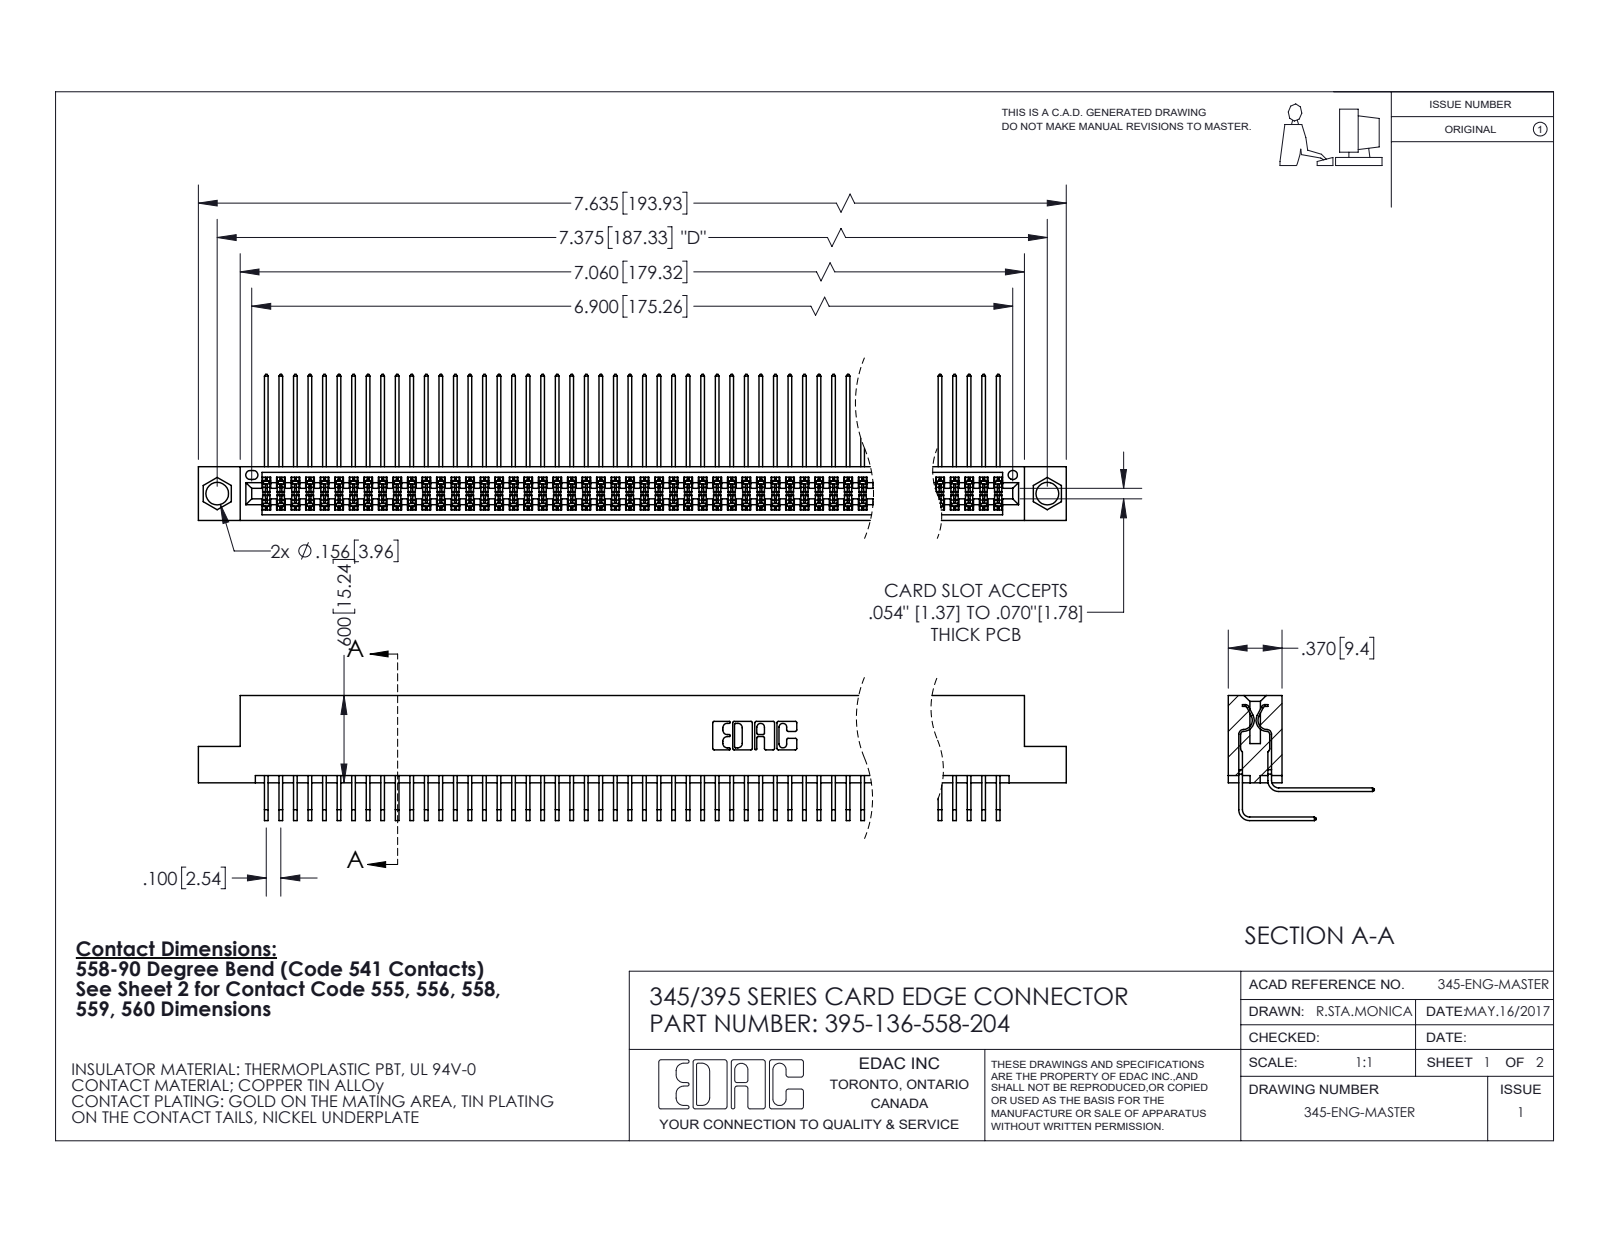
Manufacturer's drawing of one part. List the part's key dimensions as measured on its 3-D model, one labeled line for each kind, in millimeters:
Part name (STEP PRODUCT): 345 Part_Flush Mounting Lugs - 0.156 Dia-TI; 345-292-001_558 559 Tail - 1; 395-136-558-204; 345-292-001_558 Tail - 2
STEP written by: SolidWorks 2020 (CONFIG_CONTROL_DESIGN)
Units: millimetres
Bodies: 137 solids, 7212 faces (4854 planar, 2358 cylindrical, 0 other)
Overall size (bounding box): 193.9 × 25.5 × 21.8
Volume: 19 760 mm³ · Surface area: 33 250 mm²
Round holes (diameter × count): ⌀4 ×2, ⌀1.6 ×1
Partial cylindrical surfaces — rounded edges, fillets, slot ends (radius × count): R0.2 ×204, R0.3 ×22, R0.2 ×6, R0.8 ×6, R0.7 ×3, R0.4 ×2, R0.5 ×2, R0.6 ×2
Main face-to-face distances: 1.8, 7.6, 5.1, 9.4, 2.5, 6.9, 0.6, 5.7, 0.6, 4.4
Hole centre spacings: 6.9, 181.3, 187.3
